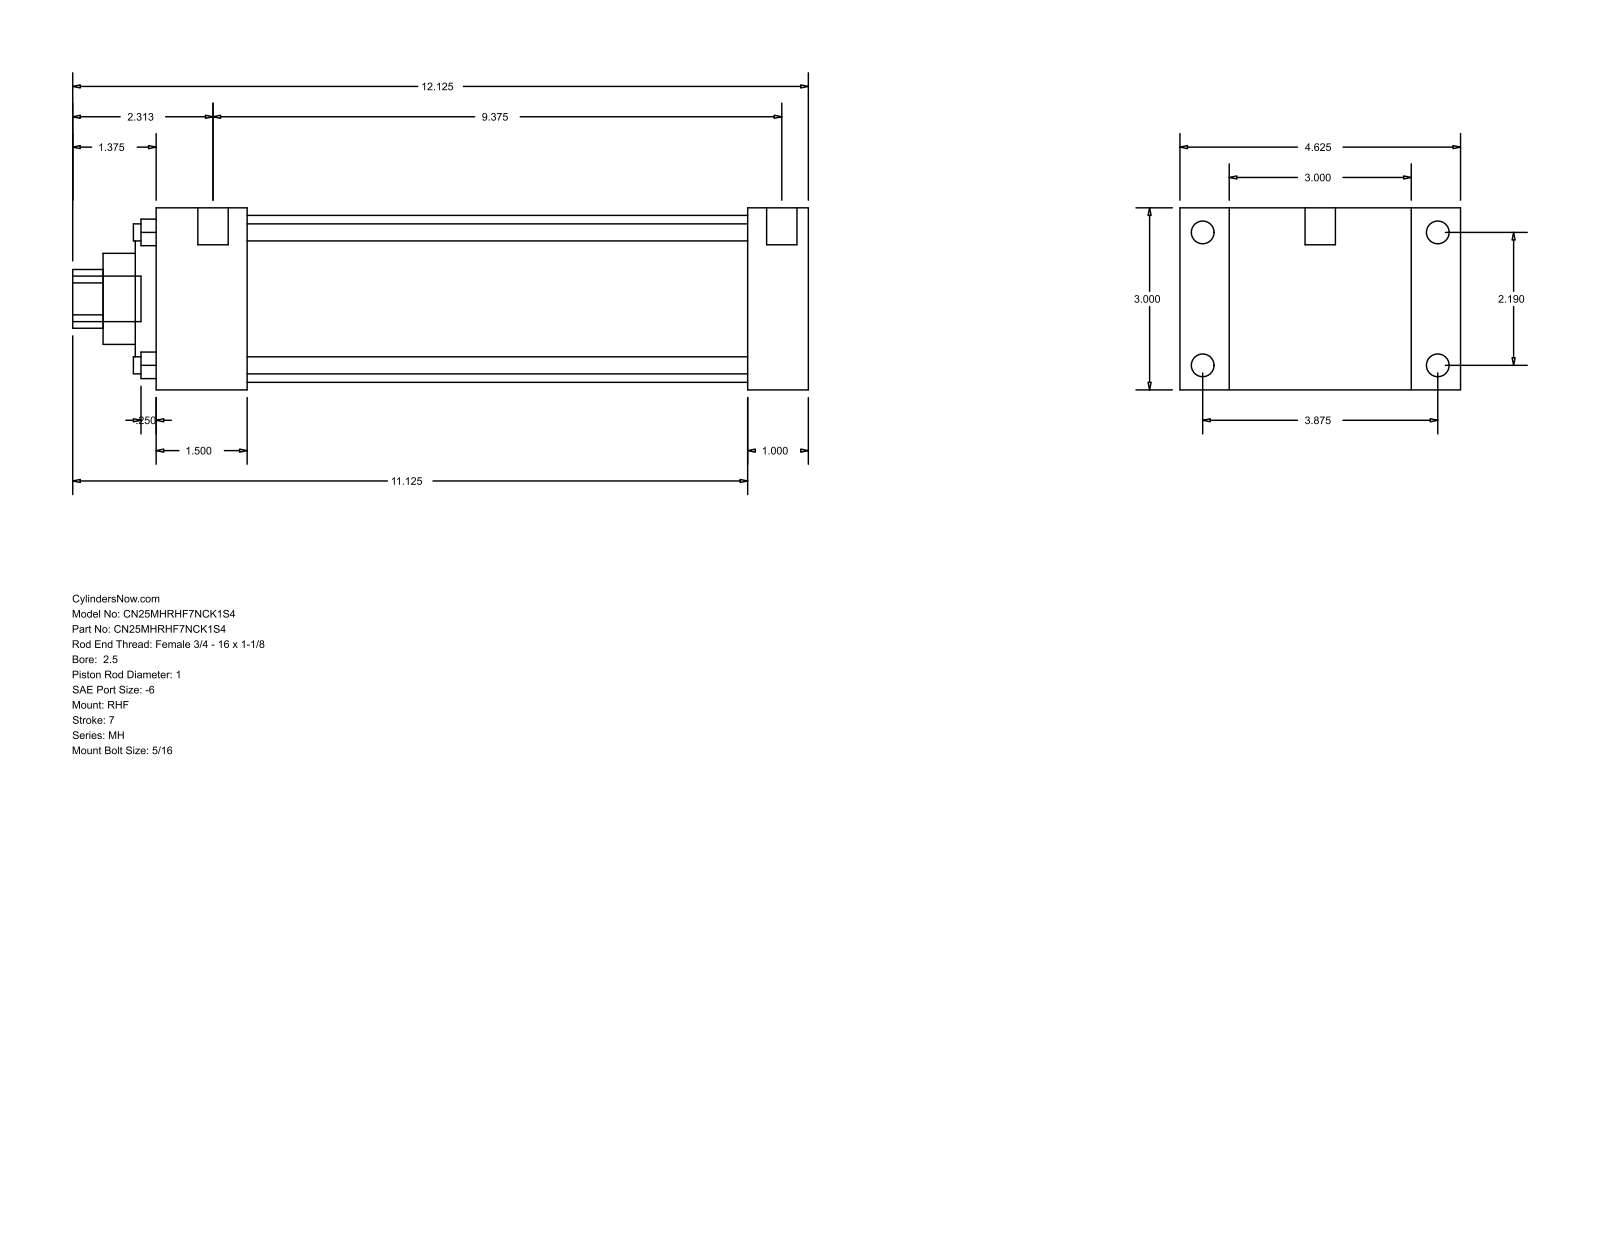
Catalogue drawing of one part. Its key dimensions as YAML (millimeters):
part_name: "MH_RHF__0250_1"
step_written_by: "GSSL Pune (CONFIG_CONTROL_DESIGN)"
units: millimeters
bodies: {solids: 0, faces: 90, planar: 61, cylindrical: 29, other: 0}
overall_size: [307.98, 117.47, 76.2]
round_holes:
  - {diameter: 7.14, count: 4}
  - {diameter: 25.4, count: 1}
  - {diameter: 38.1, count: 1}
  - {diameter: 60.33, count: 1}
  - {diameter: 69.85, count: 1}
round_bosses_or_shafts:
  - {diameter: 9.53, count: 4}
  - {diameter: 5.56, count: 4}
  - {diameter: 12.7, count: 2}
  - {diameter: 19.05, count: 1}
partial_cylinders:
  - {radius: 12.29, count: 1}
face_to_face_distances: [76.2, 25.41, 20.64, 96.84, 247.65, 273.06, 117.48, 38.11, 209.54, 234.95]
hole_center_spacings: [39.33, 55.62, 78.66]
